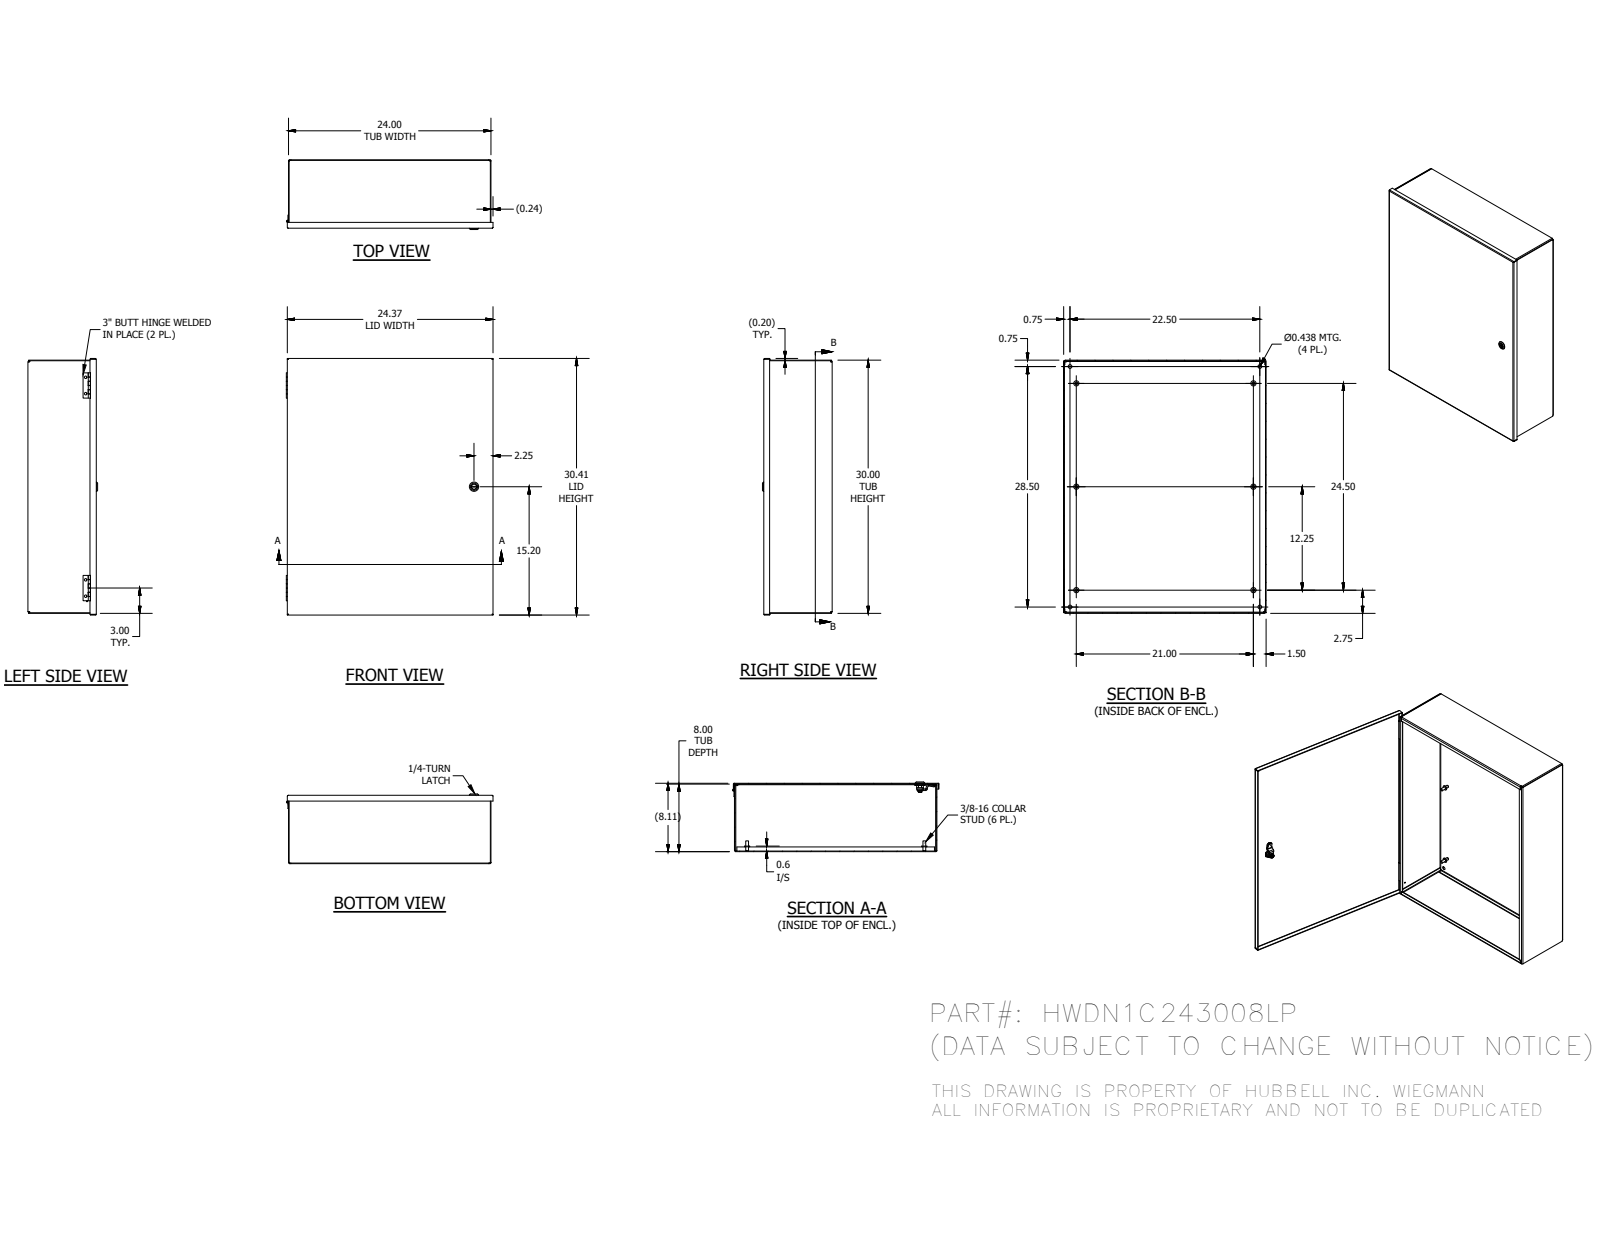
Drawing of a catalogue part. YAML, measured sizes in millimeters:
part_name: "N1C243008LPBLR; N1C2408LPTB; N1C2430LPLID; 1000-101-GPF_GPD (+8 more)"
step_written_by: "Autodesk Inventor 2016 (AUTOMOTIVE_DESIGN)"
units: millimeters
bodies: {solids: 23, faces: 733, planar: 445, cylindrical: 218, other: 70}
overall_size: [772.32, 622.01, 228.92]
volume: 3109000
surface_area: 3323000
round_holes:
  - {diameter: 7.95, count: 4}
  - {diameter: 11.11, count: 4}
  - {diameter: 3.05, count: 1}
  - {diameter: 3.3, count: 1}
  - {diameter: 5, count: 1}
  - {diameter: 8, count: 1}
  - {diameter: 10, count: 1}
  - {diameter: 10.2, count: 1}
  - {diameter: 16.1, count: 1}
  - {diameter: 20.38, count: 1}
round_bosses_or_shafts:
  - {diameter: 15.88, count: 6}
  - {diameter: 8.38, count: 6}
  - {diameter: 28, count: 1}
  - {diameter: 27, count: 1}
  - {diameter: 23, count: 1}
  - {diameter: 19.8, count: 1}
  - {diameter: 15.8, count: 1}
  - {diameter: 15.2, count: 1}
partial_cylinders:
  - {radius: 0.3, count: 30}
  - {radius: 3.47, count: 12}
  - {radius: 1.59, count: 11}
  - {radius: 0.5, count: 10}
  - {radius: 0.79, count: 4}
  - {radius: 2.67, count: 4}
  - {radius: 4, count: 4}
  - {radius: 0.4, count: 3}
face_to_face_distances: [1.88, 223.04, 221.16, 224.92, 607.72, 760.12, 605.84, 609.6, 758.24, 762]
hole_center_spacings: [49.28, 363.37, 571.5, 609.6, 649.63, 723.9, 922.3, 15.51]
